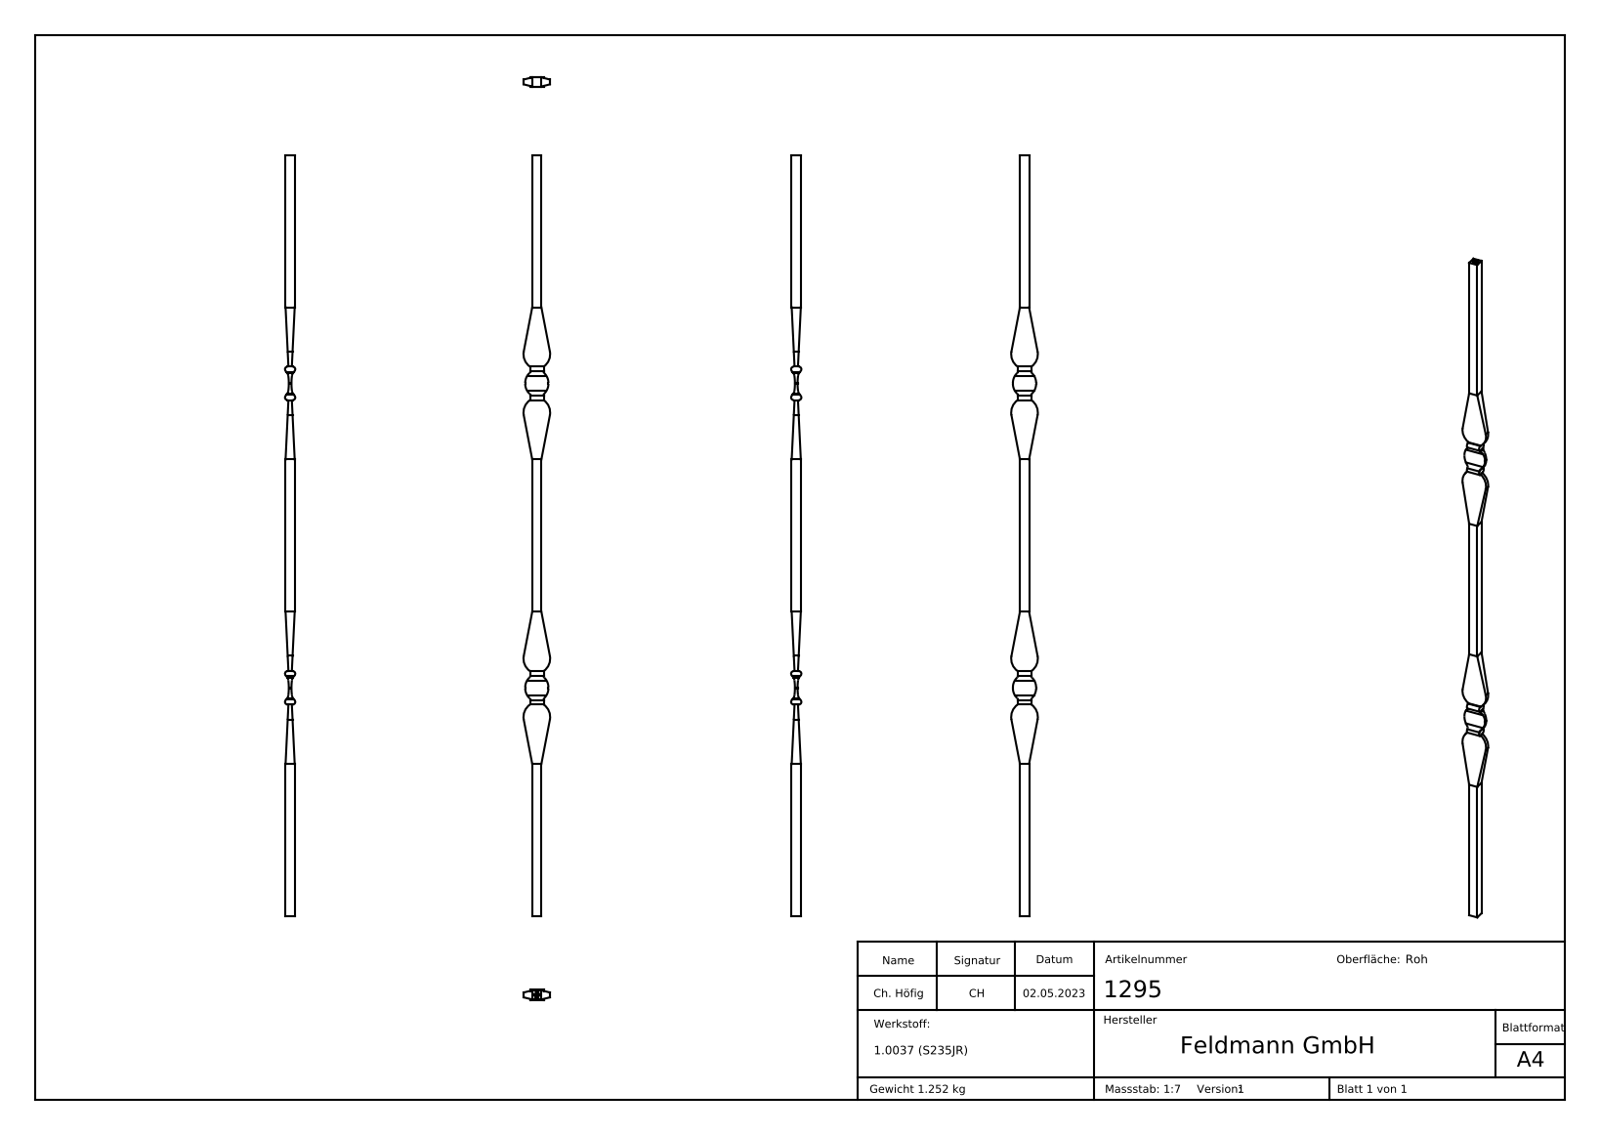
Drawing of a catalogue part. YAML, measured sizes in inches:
part_name: "1295"
step_written_by: "SolidWorks 2018 (CONFIG_CONTROL_DESIGN)"
units: inches
bodies: {solids: 1, faces: 299, planar: 164, cylindrical: 44, other: 91}
overall_size: [39.37, 1.378, 0.531]
volume: 9.792
surface_area: 87.19
partial_cylinders:
  - {radius: 0.077, count: 8}
  - {radius: 0.138, count: 8}
  - {radius: 0.394, count: 8}
  - {radius: 0.709, count: 8}
  - {radius: 0.78, count: 8}
  - {radius: 2.982, count: 4}
face_to_face_distances: [0.472, 0.094, 0.756, 0.85, 0.662, 1.952, 2.976, 4.928, 1.024, 0.118]
